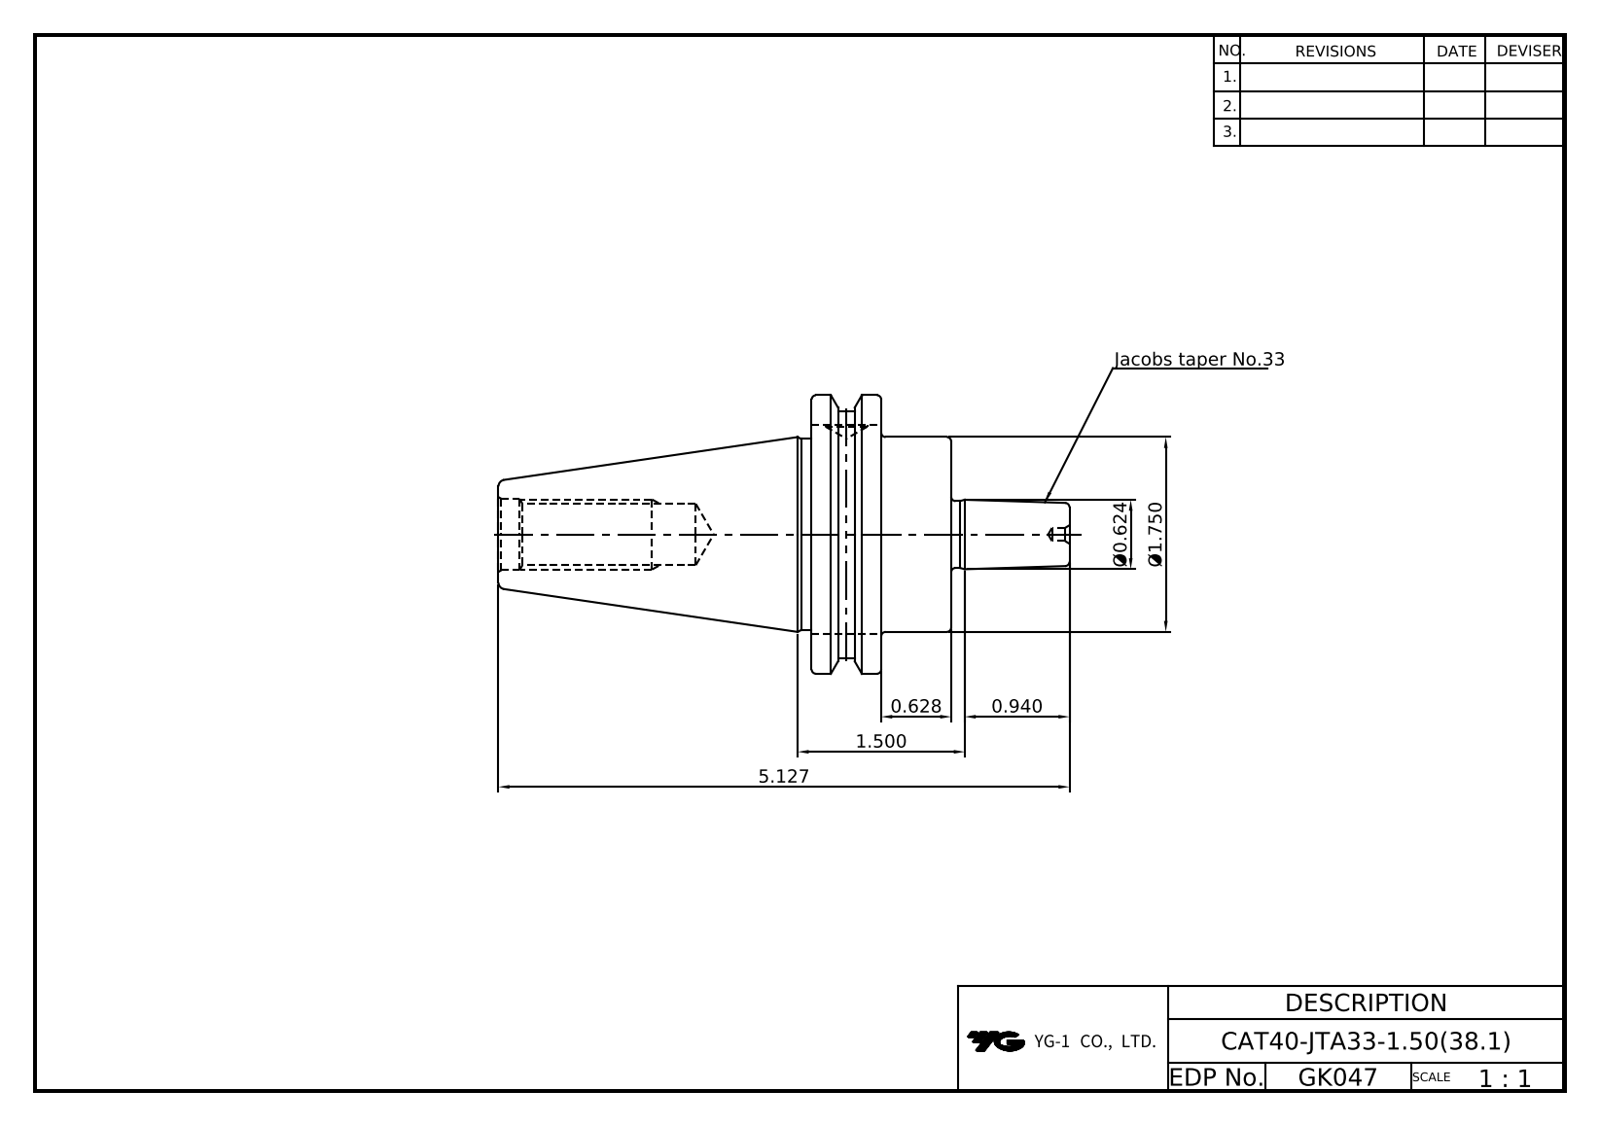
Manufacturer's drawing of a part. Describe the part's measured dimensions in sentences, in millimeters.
The part is named "CAT40-JTA33-1.50(20231109)". Its 3-D file was written by "Autodesk Inventor 2024 (AUTOMOTIVE_DESIGN)". It is 1 solid with 61 faces: 28 planar, 12 cylindrical and 21 other. Overall it measures 130.23 by 63.5 by 61.09 millimeters. Its volume is 136 363 cubic millimeters and its surface area 21 948 square millimeters. Round holes: 1 of diameter 9.53, 1 of diameter 13.39, 1 of diameter 16.3. Round bosses or shafts: 1 of diameter 63.5, 1 of diameter 56.3, 1 of diameter 44.45, 1 of diameter 43.6, 1 of diameter 15.25. The main face-to-face distances are 31.83, 15.88, 15.95, 47.6, 16.38, 71.42, 87.3, 103.25, 130.23, 58.81.
